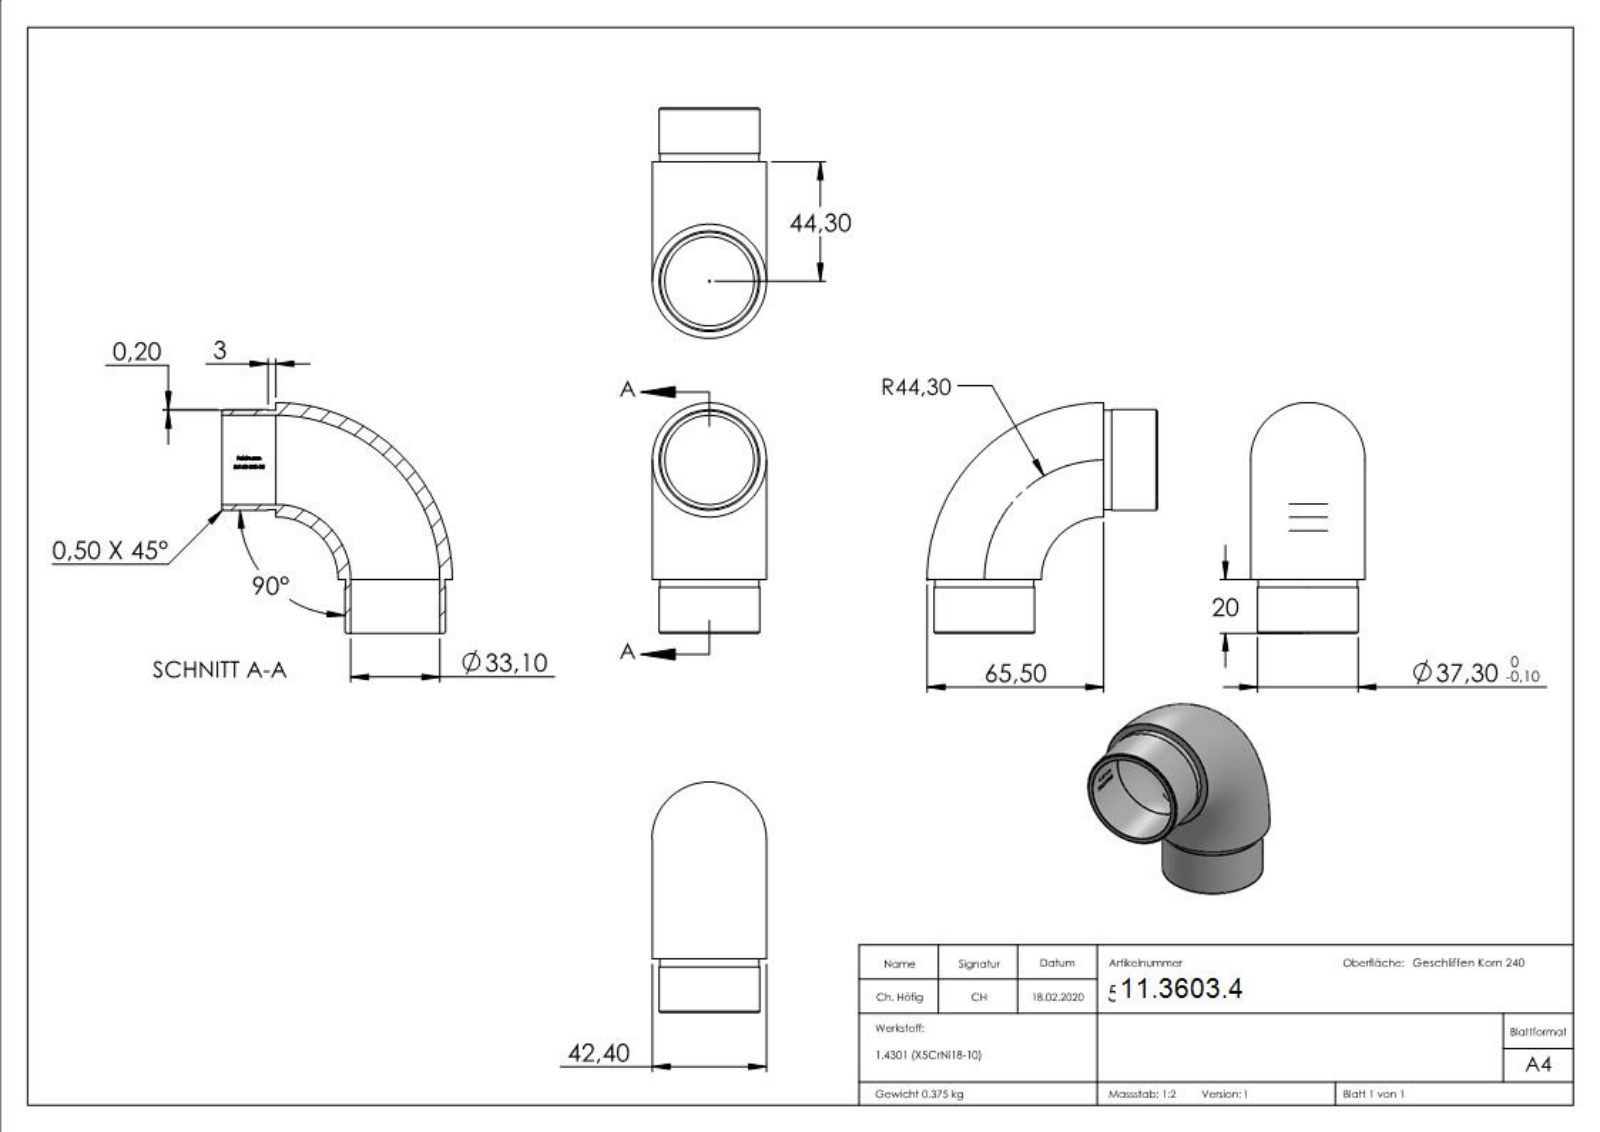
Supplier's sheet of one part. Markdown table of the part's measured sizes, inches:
| quantity | value |
| --- | --- |
| part name | 56160-320-25 |
| STEP written by | SolidWorks 2015 (CONFIG_CONTROL_DESIGN) |
| units | inches |
| bodies | 1 solid, 270 faces (107 planar, 33 cylindrical, 130 other) |
| overall size | 3.366 × 3.366 × 1.669 |
| volume | 2.898 in³ |
| surface area | 41.05 in² |
| round holes (diameter × count) | 1.303 × 2 |
| round bosses / shafts (diameter × count) | 1.469 × 2, 1.453 × 2 |
| partial cylindrical surfaces (radius × count) | 0.656 × 1 |
| main face-to-face distances | 0.787, 0.669, 0.118, 0.047, 0.052, 0.117, 0.015, 0.08, 0.144, 0.129 |
